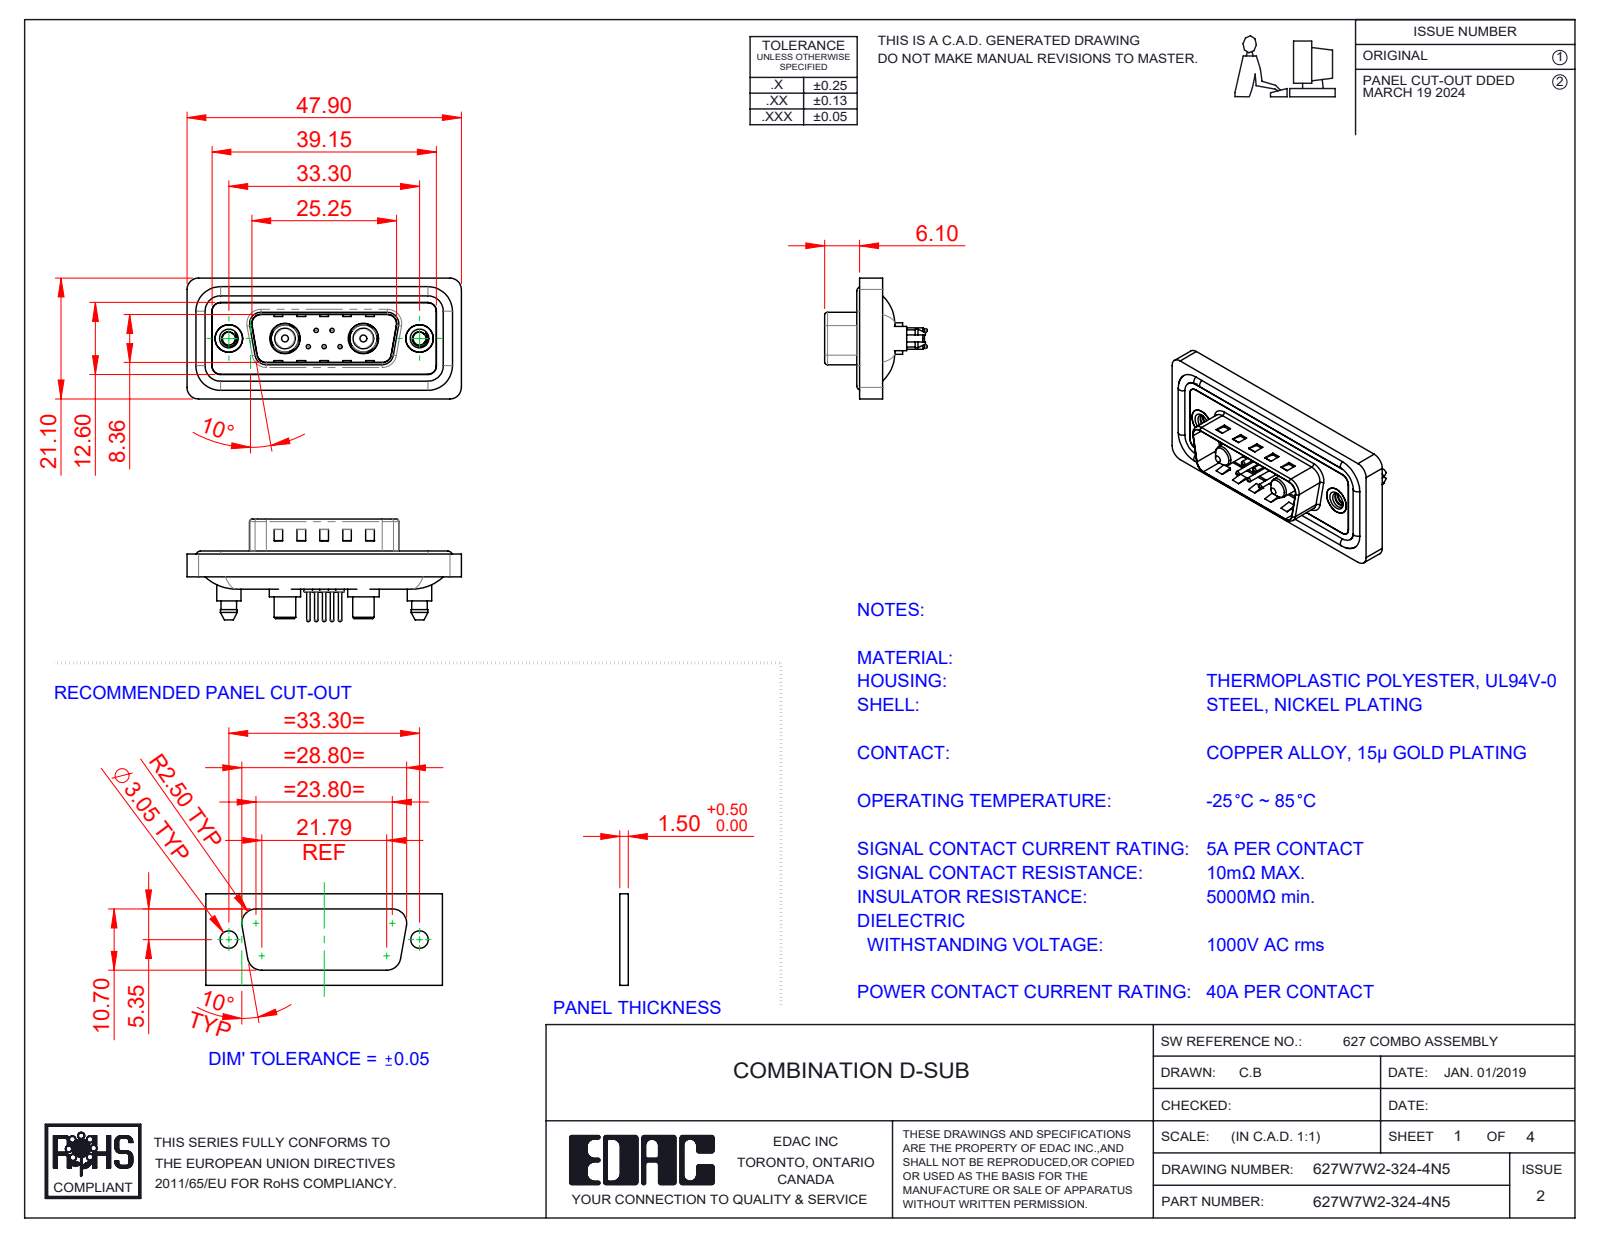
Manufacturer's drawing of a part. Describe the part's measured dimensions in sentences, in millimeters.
The part is named "627Combo Housing_7W2; Power Pin_40A S; 627Combo Contact Row 2_24; 627Combo Waterproof Housing_15 Contacts (+5 more)". Its 3-D file was written by "SolidWorks 2023 (CONFIG_CONTROL_DESIGN)". It is 16 solids with 760 faces: 248 planar, 324 cylindrical and 188 other. Overall it measures 47.9 by 21.1 by 17.9 millimeters. Its volume is 5 687 cubic millimeters and its surface area 9 148 square millimeters. Round holes: 5 of diameter 0.75, 5 of diameter 1.6, 5 of diameter 2, 2 of diameter 2.26, 2 of diameter 4, 2 of diameter 4.8, 2 of diameter 4.85, 2 of diameter 5, 2 of diameter 5.3. Round bosses or shafts: 5 of diameter 1.5, 5 of diameter 0.6, 4 of diameter 1.6, 2 of diameter 5.5, 2 of diameter 5.4, 2 of diameter 5.2, 2 of diameter 4.9, 2 of diameter 4.75. Partial cylindrical surfaces (rounded edges, fillets, slot ends): 28 of radius 1.5, 20 of radius 2, 10 of radius 1.6, 8 of radius 0.5, 4 of radius 0.25, 4 of radius 0.6, 4 of radius 0.65, 4 of radius 0.9. The main face-to-face distances are 0.4, 1.1, 1.6, 1.5, 3.1, 0.5, 2.9, 0.7, 0.82, 9.58. The hole center spacings are 3.16, 2.77, 9.8, 23.5, 4.31, 4.33, 5.03, 5.04.
